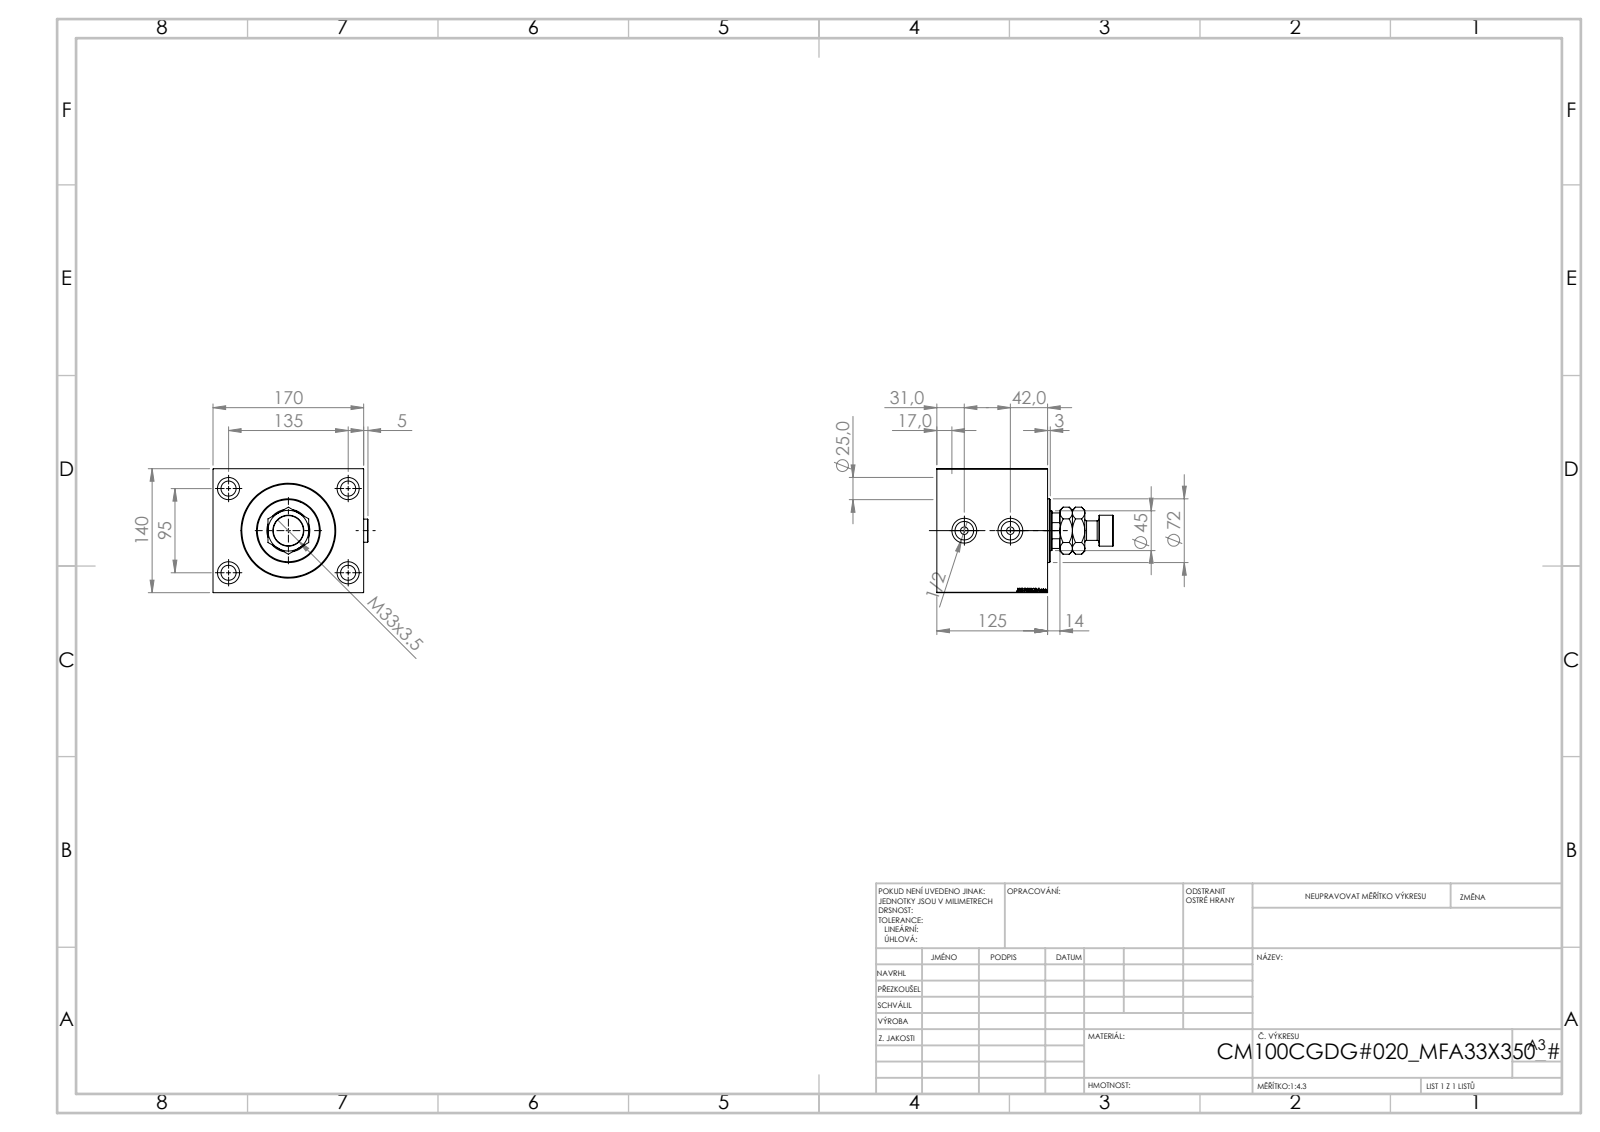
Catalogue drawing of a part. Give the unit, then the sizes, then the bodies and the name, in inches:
Units: inches
Overall size (bounding box): 7.835 × 6.886 × 5.512
Round holes (diameter × count): ⌀0.669 ×4, ⌀0.984 ×4, ⌀0.335 ×2, ⌀0.825 ×2, ⌀1.102 ×2, ⌀1.24 ×1, ⌀1.772 ×1, ⌀1.909 ×1, ⌀3.937 ×1, ⌀4.016 ×1, ⌀4.134 ×1
Round bosses / shafts (diameter × count): ⌀1.024 ×2, ⌀2.835 ×1, ⌀1.378 ×1, ⌀0.866 ×1
Partial cylindrical surfaces — rounded edges, fillets, slot ends (radius × count): R0.866 ×1
Main face-to-face distances: 5.512, 4.921, 2.913, 6.693, 2.008, 0.85, 1.157, 4.071, 0.394, 1.244
Hole centre spacings: 3.25, 3.74, 5.315, 6.499, 2.047
Volume: 171.2 in³ · Surface area: 386.9 in²
Bodies: 6 solids, 969 faces (459 planar, 80 cylindrical, 430 other)
Part name (STEP PRODUCT): Zatka_OIL_PORT; V450CM_C_Body; V450CM_VC_B; MFA (+1 more)
STEP written by: SolidWorks 2019 (CONFIG_CONTROL_DESIGN)
